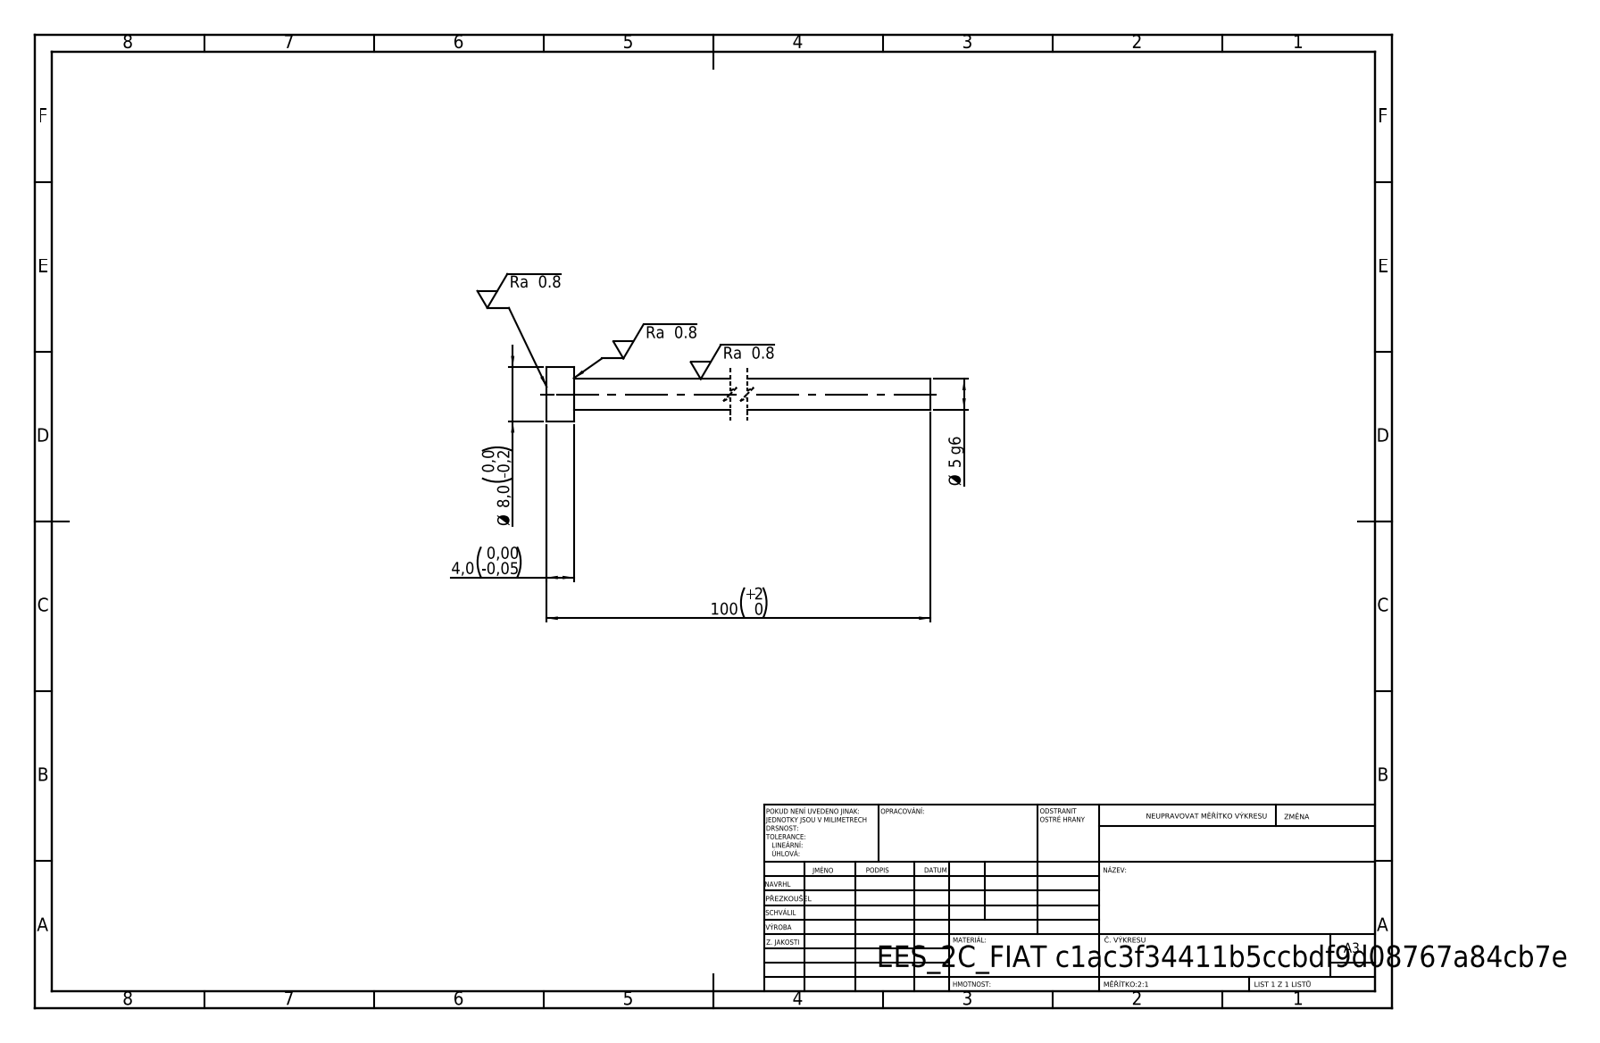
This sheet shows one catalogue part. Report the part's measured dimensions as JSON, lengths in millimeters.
{"step_written_by": "SolidWorks 2019 (CONFIG_CONTROL_DESIGN)", "units": "millimeters", "bodies": {"solids": 1, "faces": 7, "planar": 3, "cylindrical": 4, "other": 0}, "overall_size": [100, 8, 8], "volume_mm3": 1728, "surface_area_mm2": 1558, "round_bosses_or_shafts": [[8, 1], [4.5, 1]], "face_to_face_distances": [4, 100, 96]}
